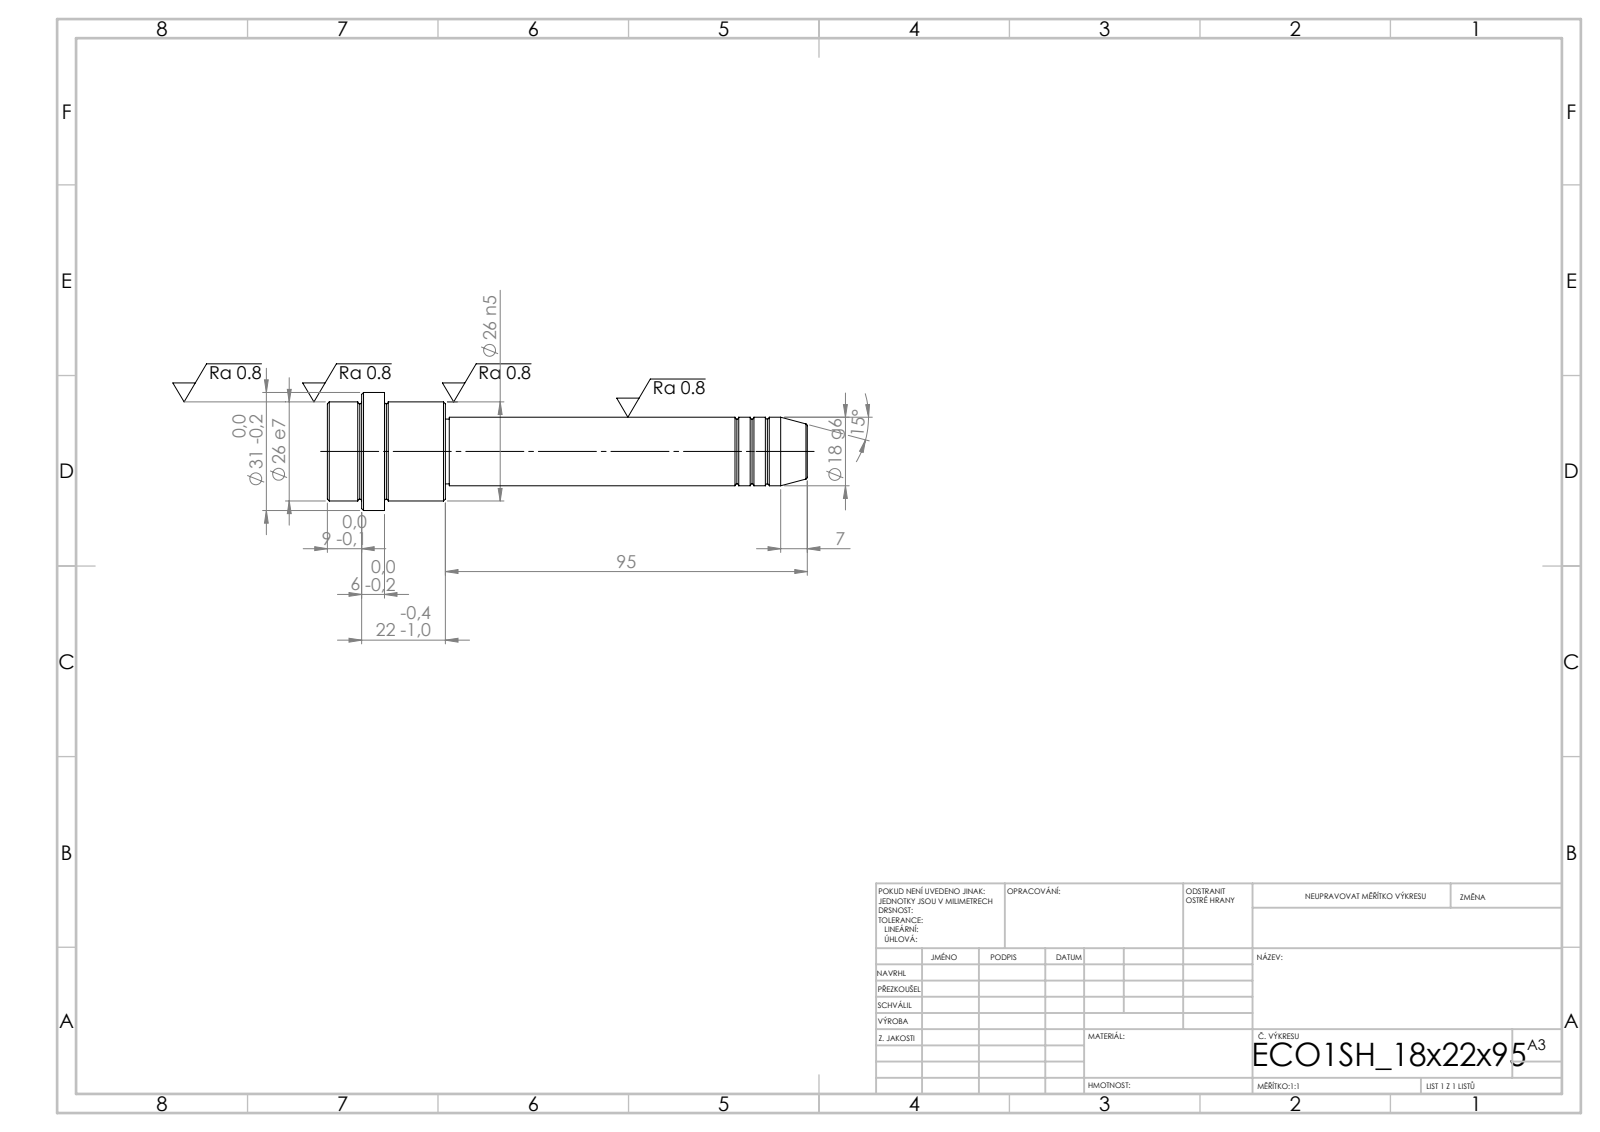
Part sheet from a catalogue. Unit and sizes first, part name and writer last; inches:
Units: inches
Overall size (bounding box): 4.961 × 1.22 × 1.22
Round bosses / shafts (diameter × count): ⌀1.22 ×1, ⌀1.024 ×1, ⌀0.709 ×1, ⌀0.669 ×1
Main face-to-face distances: 1.22, 0.63, 0.591, 0.866, 0.236, 0.354, 3.74, 4.37, 4.606, 4.961
Volume: 2.529 in³ · Surface area: 14.77 in²
Bodies: 1 solid, 52 faces (6 planar, 16 cylindrical, 30 other)
STEP written by: SolidWorks 2019 (CONFIG_CONTROL_DESIGN)
